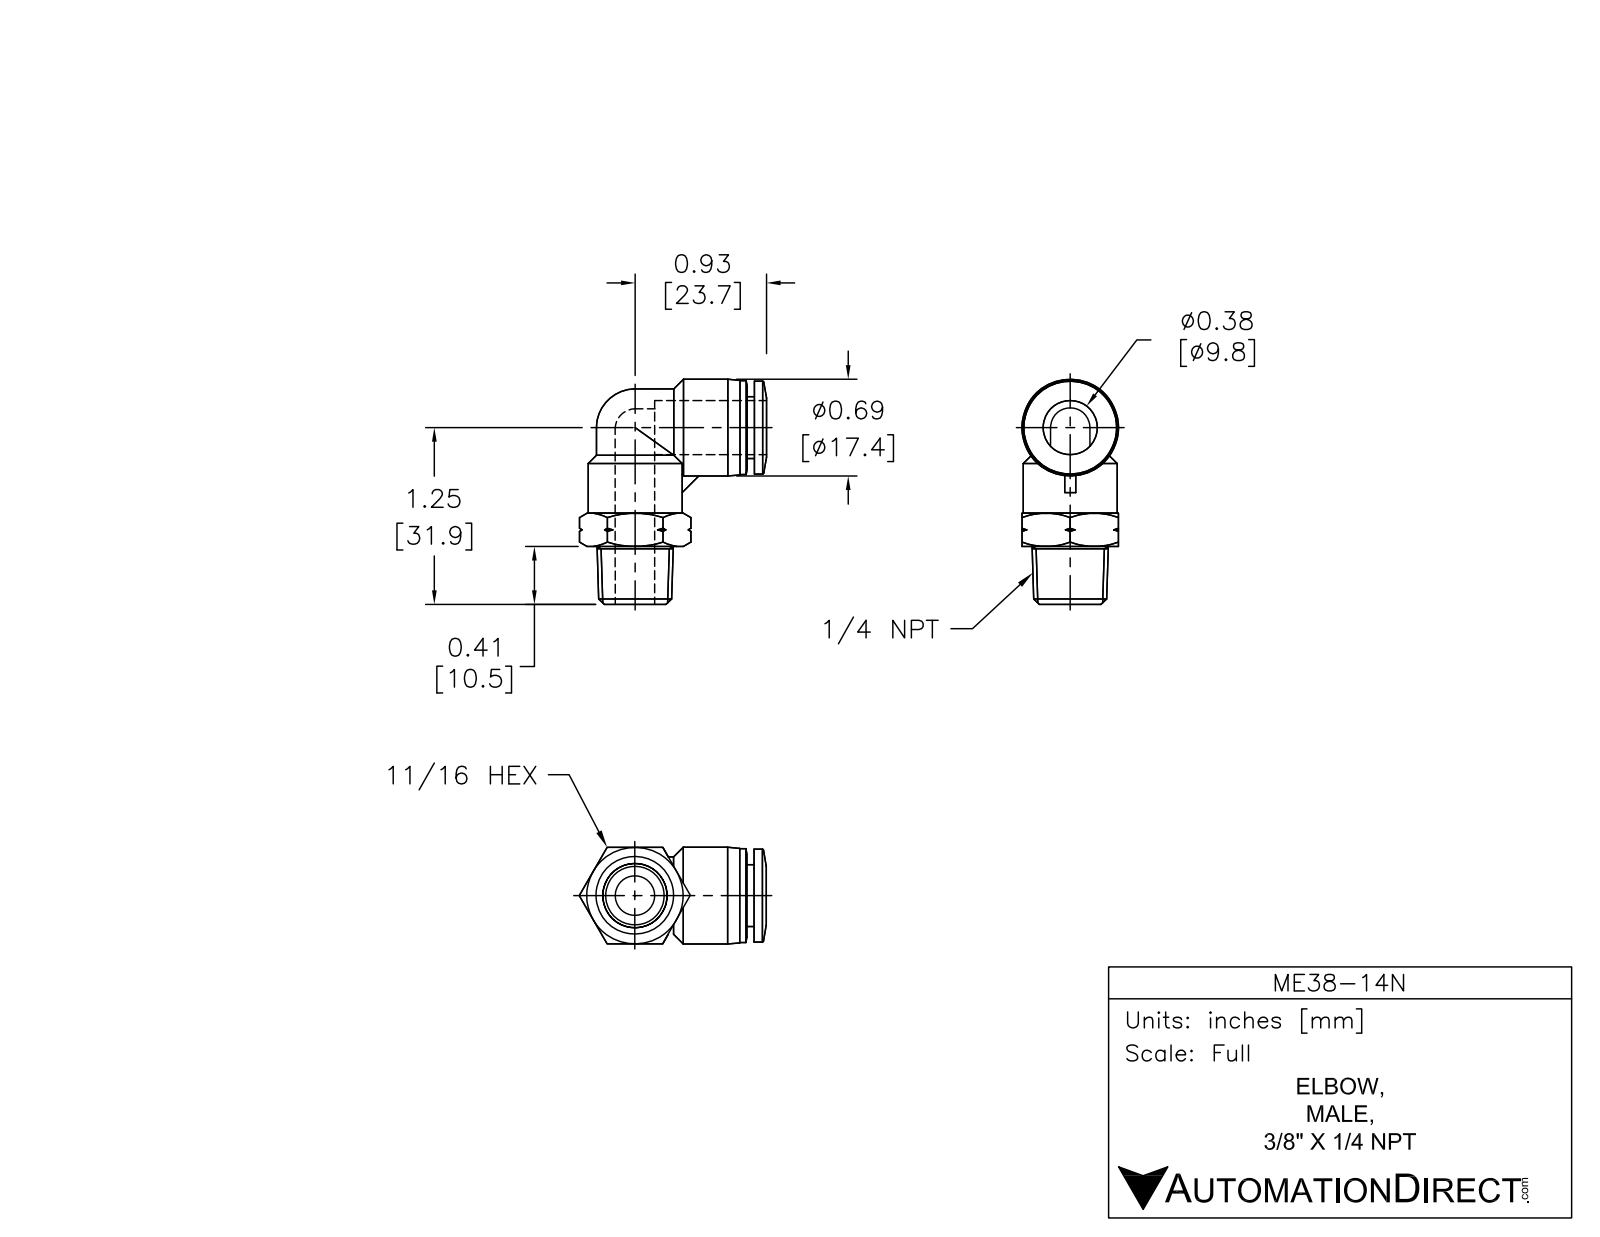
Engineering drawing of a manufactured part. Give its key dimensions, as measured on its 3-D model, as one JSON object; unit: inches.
{"part_name": "ME38-14N", "step_written_by": "SolidWorks 2015 (AUTOMOTIVE_DESIGN)", "units": "inches", "bodies": {"solids": 1, "faces": 83, "planar": 16, "cylindrical": 20, "other": 47}, "overall_size": [1.604, 1.363, 0.689], "volume_in3": 0.491, "surface_area_in2": 7.457, "round_holes": [[0.276, 2], [0.386, 1]], "round_bosses_or_shafts": [[0.669, 2], [0.689, 1], [0.661, 1], [0.551, 1], [0.441, 1]], "partial_cylinders_radius": [[0.276, 1]], "face_to_face_distances": [0.687, 0.051, 0.413, 0.654, 0.705, 0.65, 0.236, 0.304, 0.383, 0.079]}
